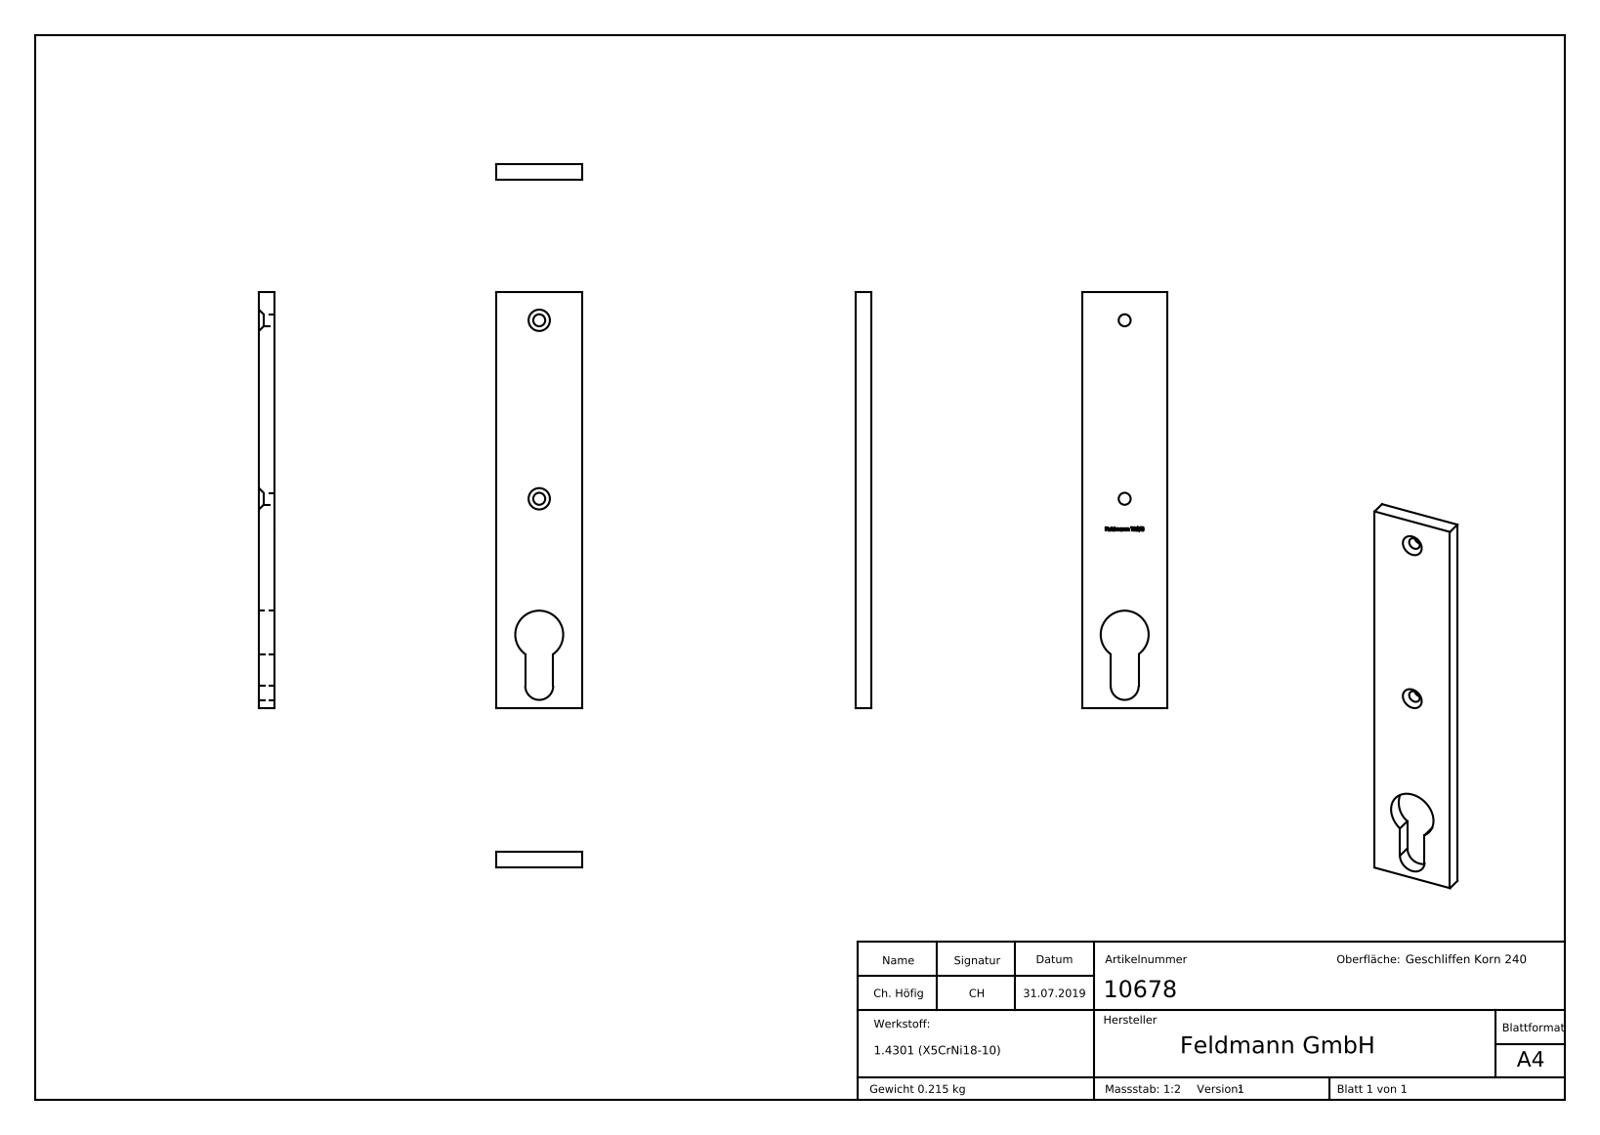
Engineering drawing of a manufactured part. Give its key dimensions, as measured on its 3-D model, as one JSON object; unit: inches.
{"part_name": "10678", "step_written_by": "SolidWorks 2015 (CONFIG_CONTROL_DESIGN)", "units": "inches", "bodies": {"solids": 1, "faces": 192, "planar": 97, "cylindrical": 8, "other": 87}, "overall_size": [6.142, 1.26, 0.236], "volume_in3": 1.662, "surface_area_in2": 18.64, "round_holes": [[0.177, 2], [0.709, 1]], "partial_cylinders_radius": [[0.207, 1]], "face_to_face_distances": [0.236, 1.26, 6.142, 0.423, 0.837, 0.413, 0.232, 0.117, 0.072, 0.015], "hole_center_spacings": [2.008, 2.638, 4.646]}
